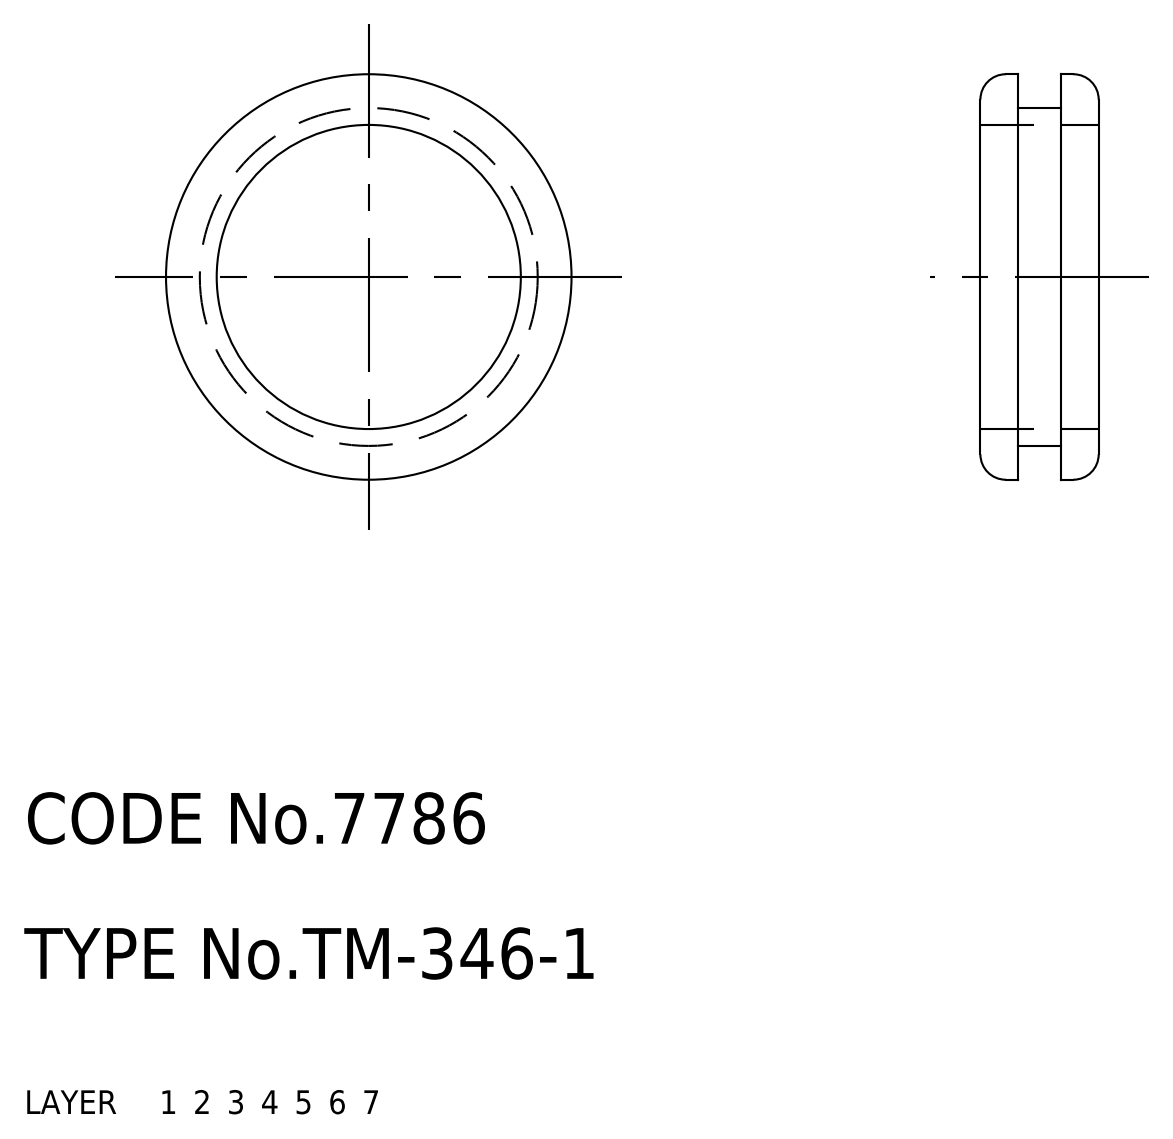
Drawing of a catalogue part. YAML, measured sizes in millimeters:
part_name: "TM_346_1"
step_written_by: "SolidWorks 2015 (AUTOMOTIVE_DESIGN)"
units: millimeters
bodies: {solids: 1, faces: 16, planar: 4, cylindrical: 8, other: 4}
overall_size: [24, 24, 7]
volume: 969
surface_area: 1465
round_holes:
  - {diameter: 18, count: 1}
round_bosses_or_shafts:
  - {diameter: 24, count: 1}
  - {diameter: 20, count: 1}
face_to_face_distances: [2.25, 4.75, 2.5, 7]
